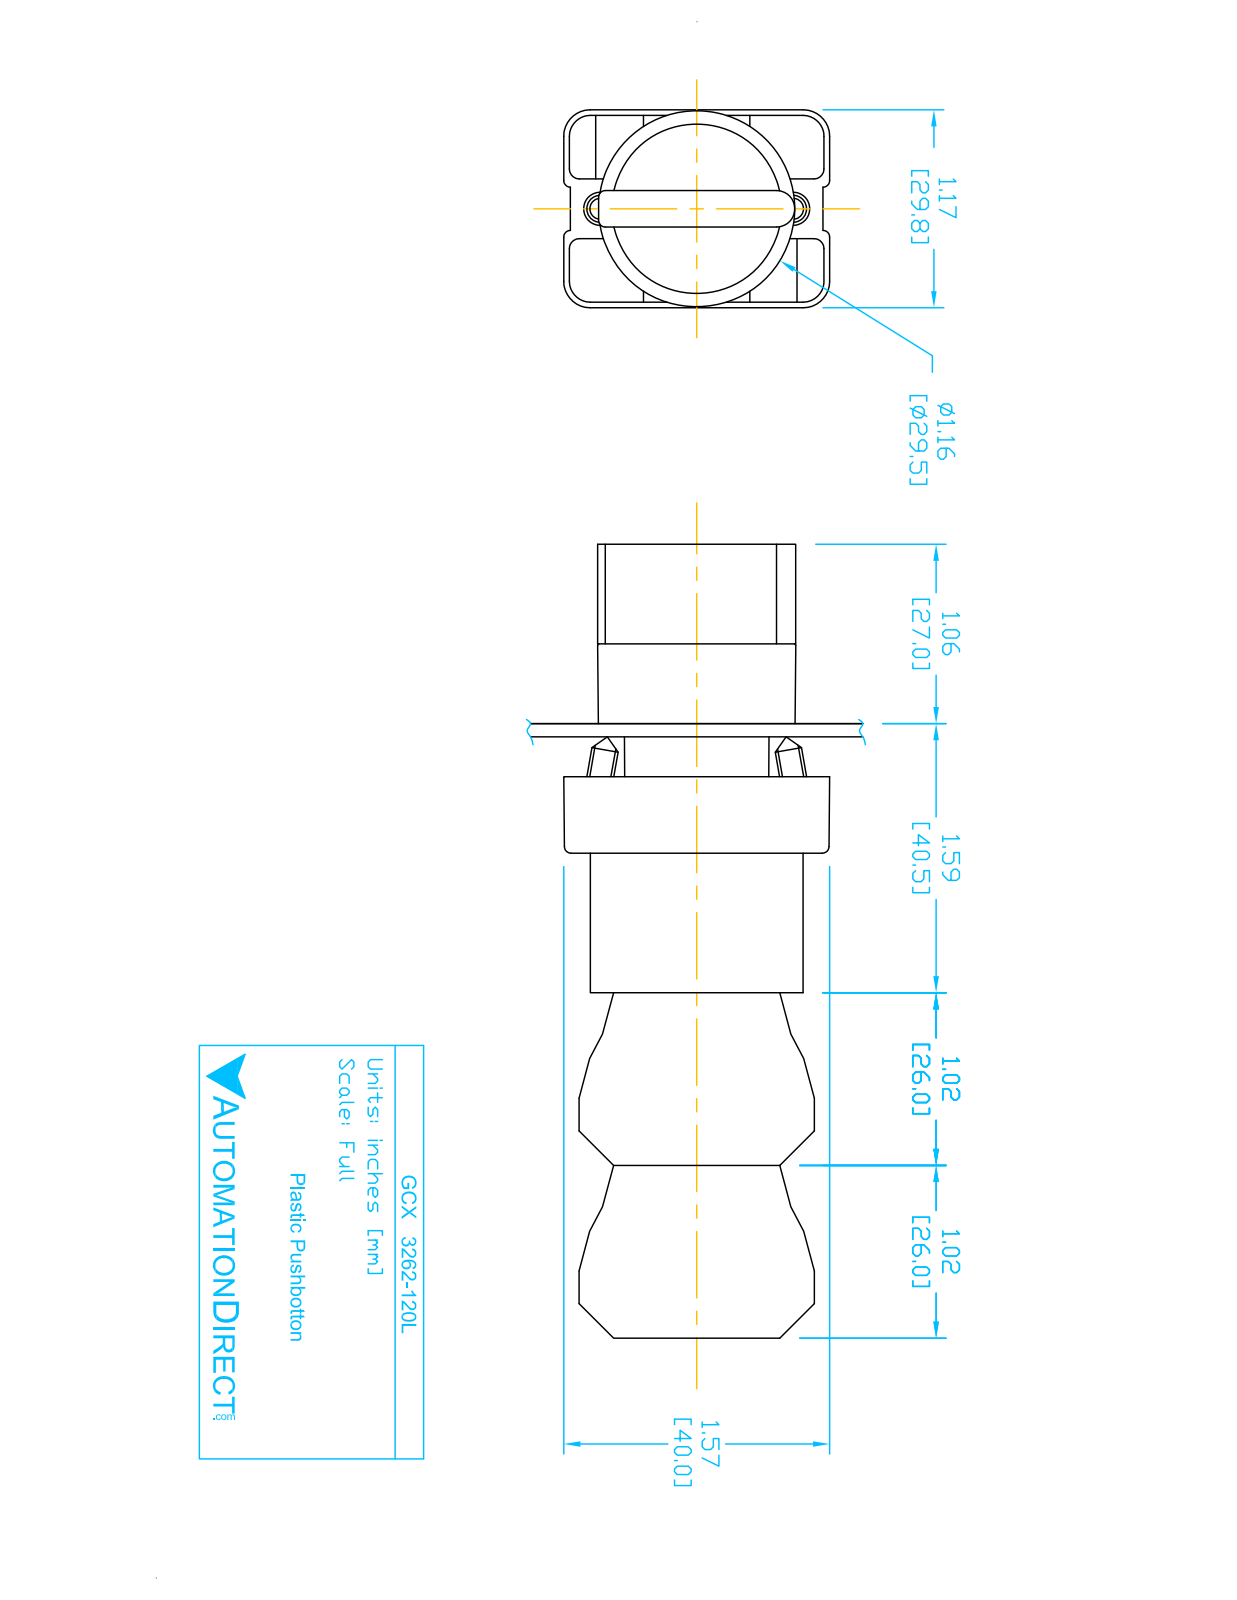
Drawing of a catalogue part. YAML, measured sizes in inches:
part_name: "ecx1040; ecx1030; ECX1050; GCX3262L OPERATOR (+2 more)"
step_written_by: "SolidWorks 2016 (AUTOMOTIVE_DESIGN)"
units: inches
bodies: {solids: 11, faces: 724, planar: 488, cylindrical: 193, other: 43}
overall_size: [4.677, 1.581, 1.177]
volume: 4.751
surface_area: 59.22
round_holes:
  - {diameter: 0.079, count: 4}
  - {diameter: 0.087, count: 2}
  - {diameter: 0.124, count: 2}
  - {diameter: 0.13, count: 2}
  - {diameter: 0.197, count: 1}
  - {diameter: 0.469, count: 1}
  - {diameter: 0.878, count: 1}
  - {diameter: 0.888, count: 1}
  - {diameter: 1.024, count: 1}
round_bosses_or_shafts:
  - {diameter: 0.157, count: 4}
  - {diameter: 1.175, count: 1}
  - {diameter: 1.004, count: 1}
  - {diameter: 0.945, count: 1}
  - {diameter: 0.856, count: 1}
  - {diameter: 0.78, count: 1}
  - {diameter: 0.504, count: 1}
partial_cylinders:
  - {radius: 0.059, count: 24}
  - {radius: 0.041, count: 12}
  - {radius: 0.124, count: 12}
  - {radius: 0.157, count: 12}
  - {radius: 0.039, count: 9}
  - {radius: 0.02, count: 2}
  - {radius: 0.063, count: 2}
  - {radius: 0.079, count: 2}
face_to_face_distances: [0.579, 0.593, 1.024, 1.171, 0.014, 0.827, 1.85, 3.043, 2.02, 1.193]
hole_center_spacings: [0.236, 1.003, 0.974, 0.472, 0.539, 0.544, 1.083, 0.484]
